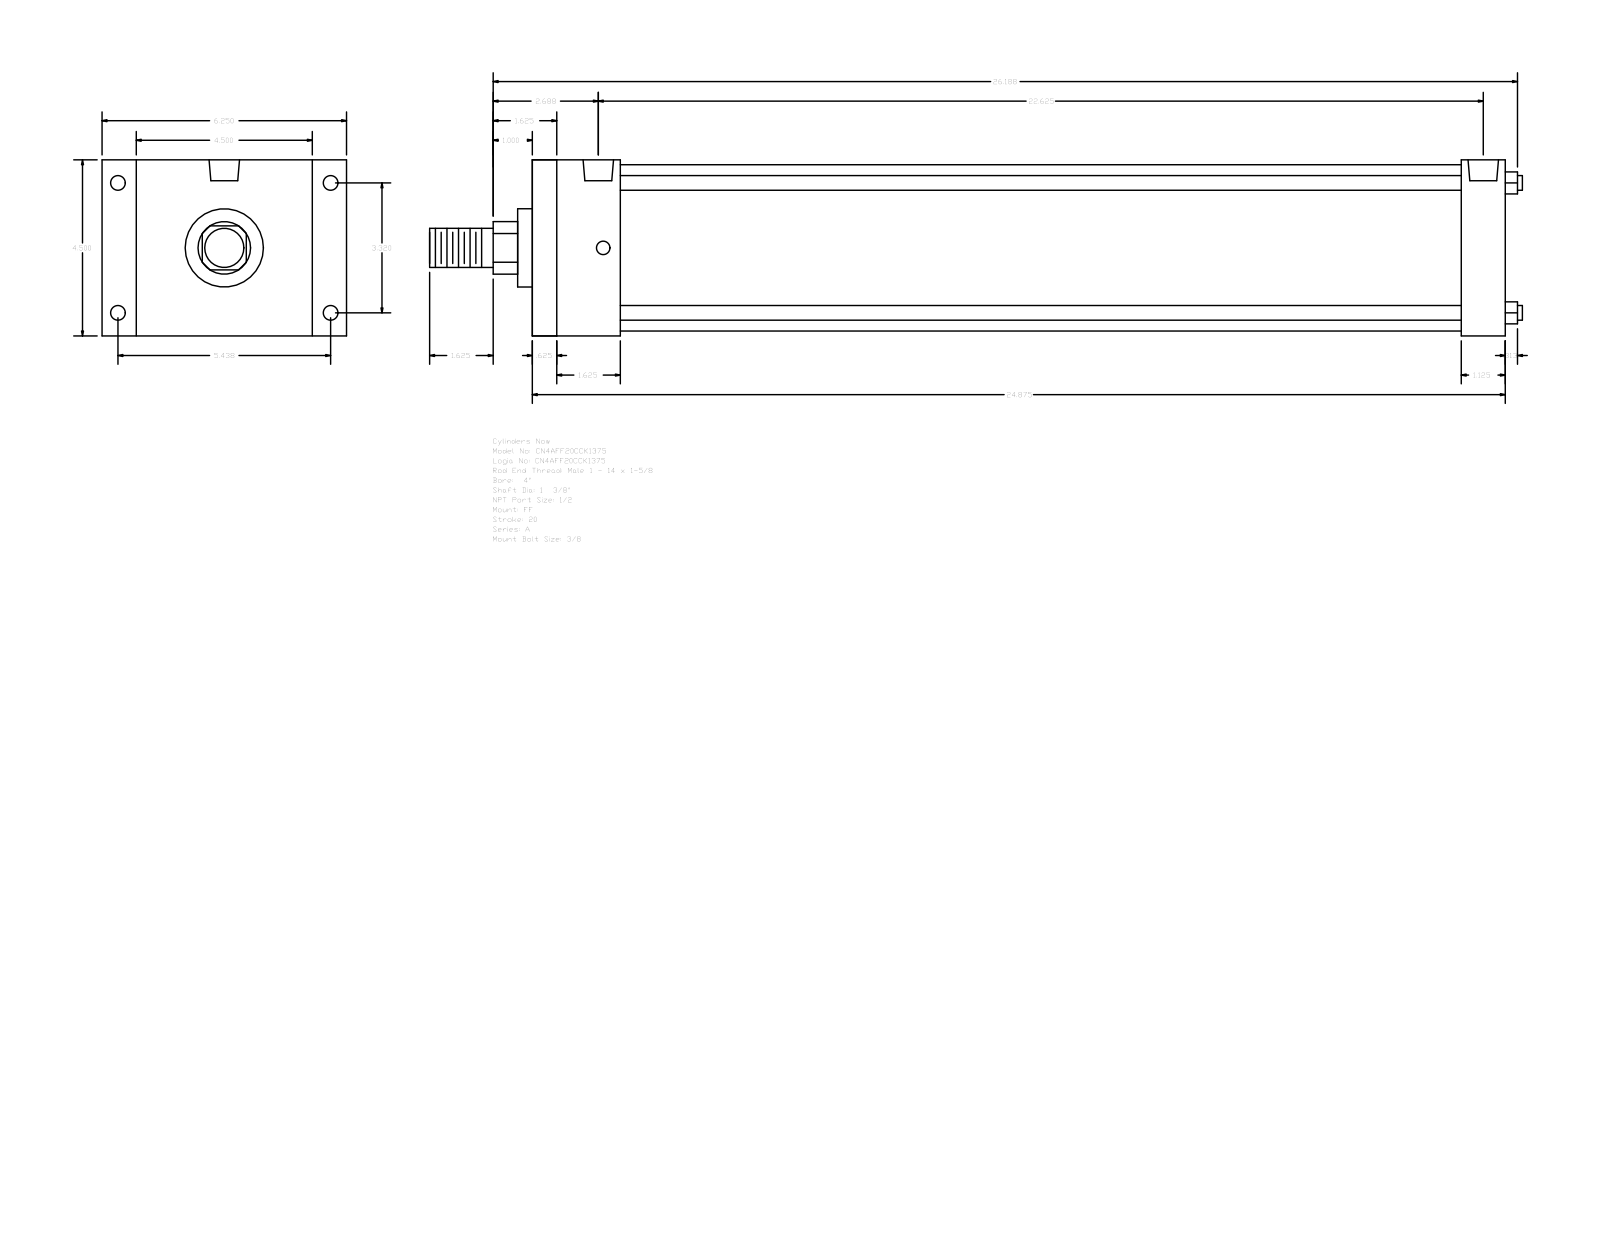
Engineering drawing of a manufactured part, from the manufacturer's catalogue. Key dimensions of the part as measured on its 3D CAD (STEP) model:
Part name (STEP PRODUCT): A_FF__0400_1.375
STEP written by: GSSL Pune (CONFIG_CONTROL_DESIGN)
Units: millimetres
Bodies: 0 solids, 92 faces (64 planar, 28 cylindrical, 0 other)
Overall size (bounding box): 709.61 × 158.75 × 114.3
Round holes (diameter × count): ⌀8.73 ×4, ⌀9.53 ×4, ⌀19.77 ×2
Round bosses / shafts (diameter × count): ⌀9.53 ×4, ⌀107.95 ×1, ⌀50.8 ×1, ⌀34.92 ×1, ⌀25.4 ×1
Partial cylindrical surfaces — rounded edges, fillets, slot ends (radius × count): R17.06 ×1
Main face-to-face distances: 114.3, 631.83, 15.87, 615.96, 57.15, 28.58, 22.23, 136.53, 603.25, 587.38
Hole centre spacings: 3.18, 84.32, 138.12, 161.82, 568.32, 571.5, 574.68
